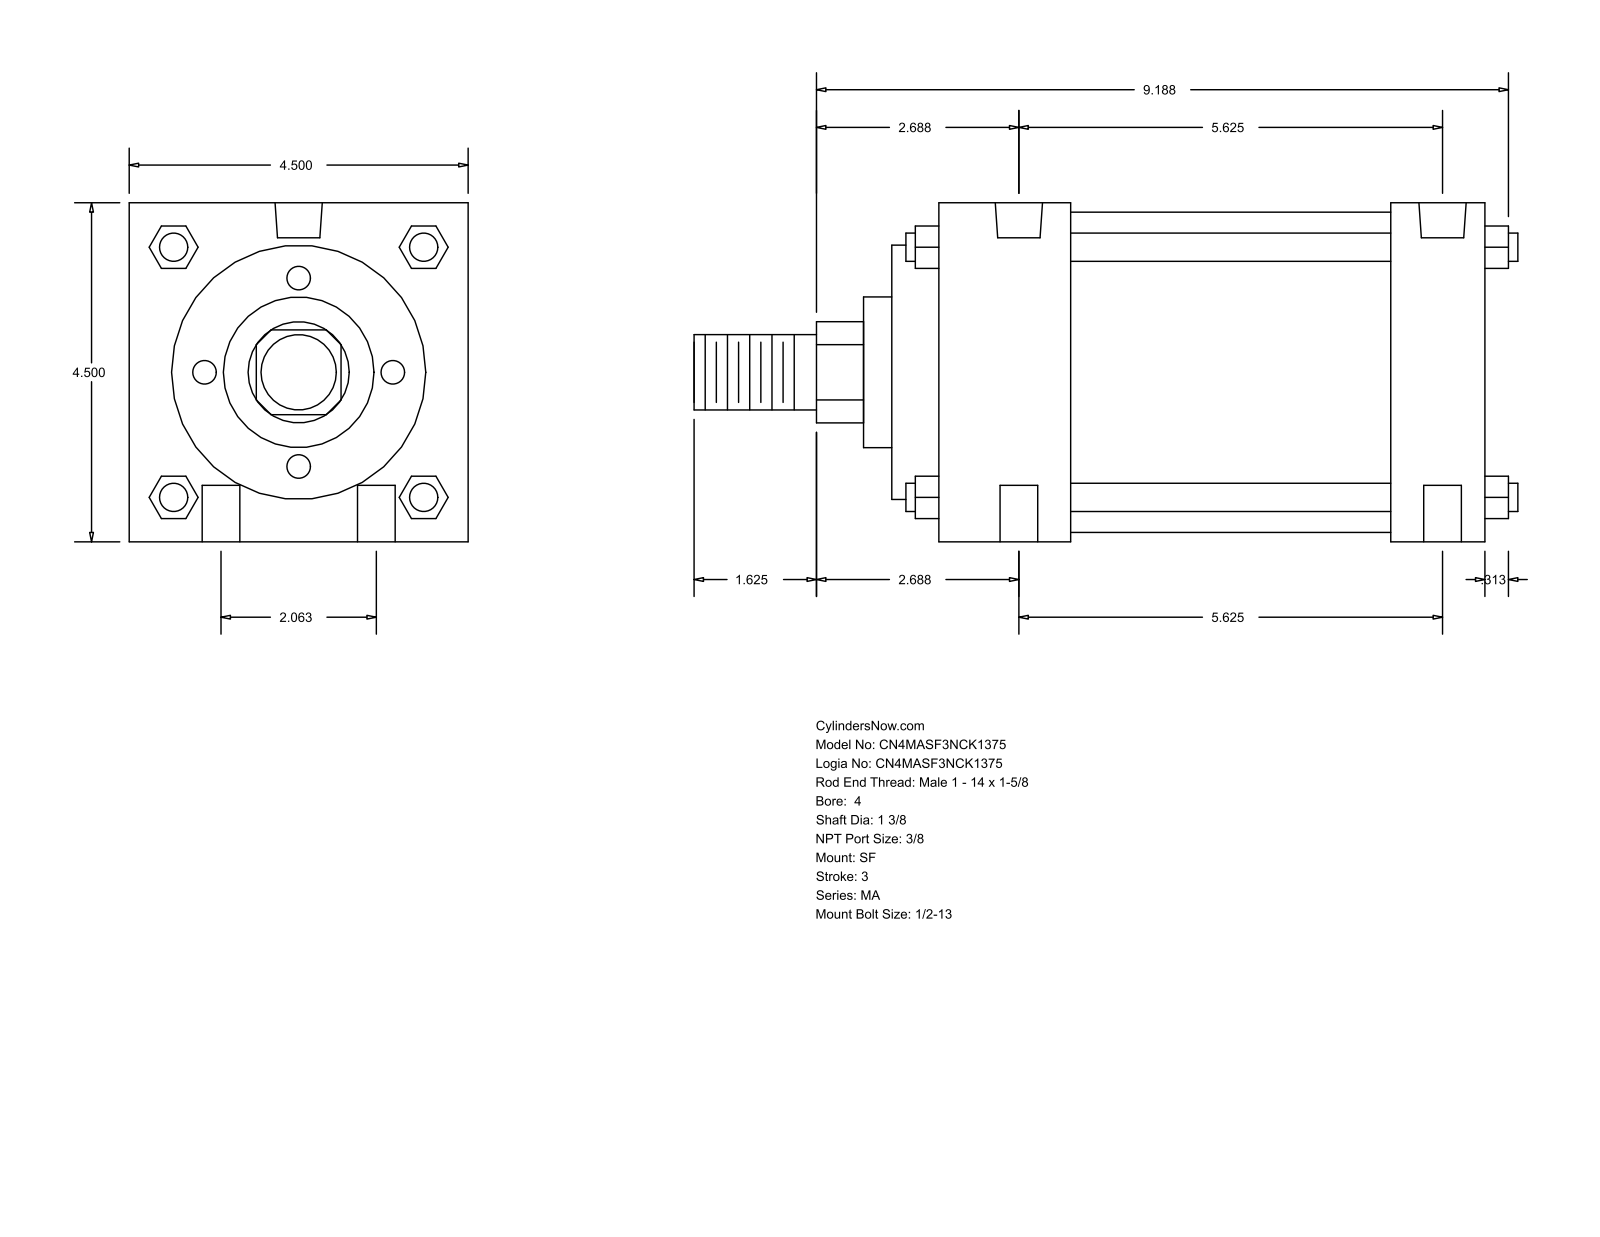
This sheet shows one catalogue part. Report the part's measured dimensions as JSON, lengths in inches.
{"part_name": "MA_SF__0400_1.375", "step_written_by": "GSSL Pune (CONFIG_CONTROL_DESIGN)", "units": "inches", "bodies": {"solids": 0, "faces": 126, "planar": 95, "cylindrical": 31, "other": 0}, "overall_size": [10.937, 4.5, 4.5], "round_holes": [[0.5, 4], [0.437, 2], [0.627, 2]], "round_bosses_or_shafts": [[0.375, 4], [4.25, 1], [3.375, 1], [2, 1], [1.375, 1], [1, 1]], "partial_cylinders_radius": [[0.672, 1]], "face_to_face_distances": [4.5, 7.25, 0.625, 7.875, 6.625, 6, 1.25, 2.375, 1.75, 4.25], "hole_center_spacings": [1.031, 5.719, 5.625, 2.062, 5.991, 5.25]}
